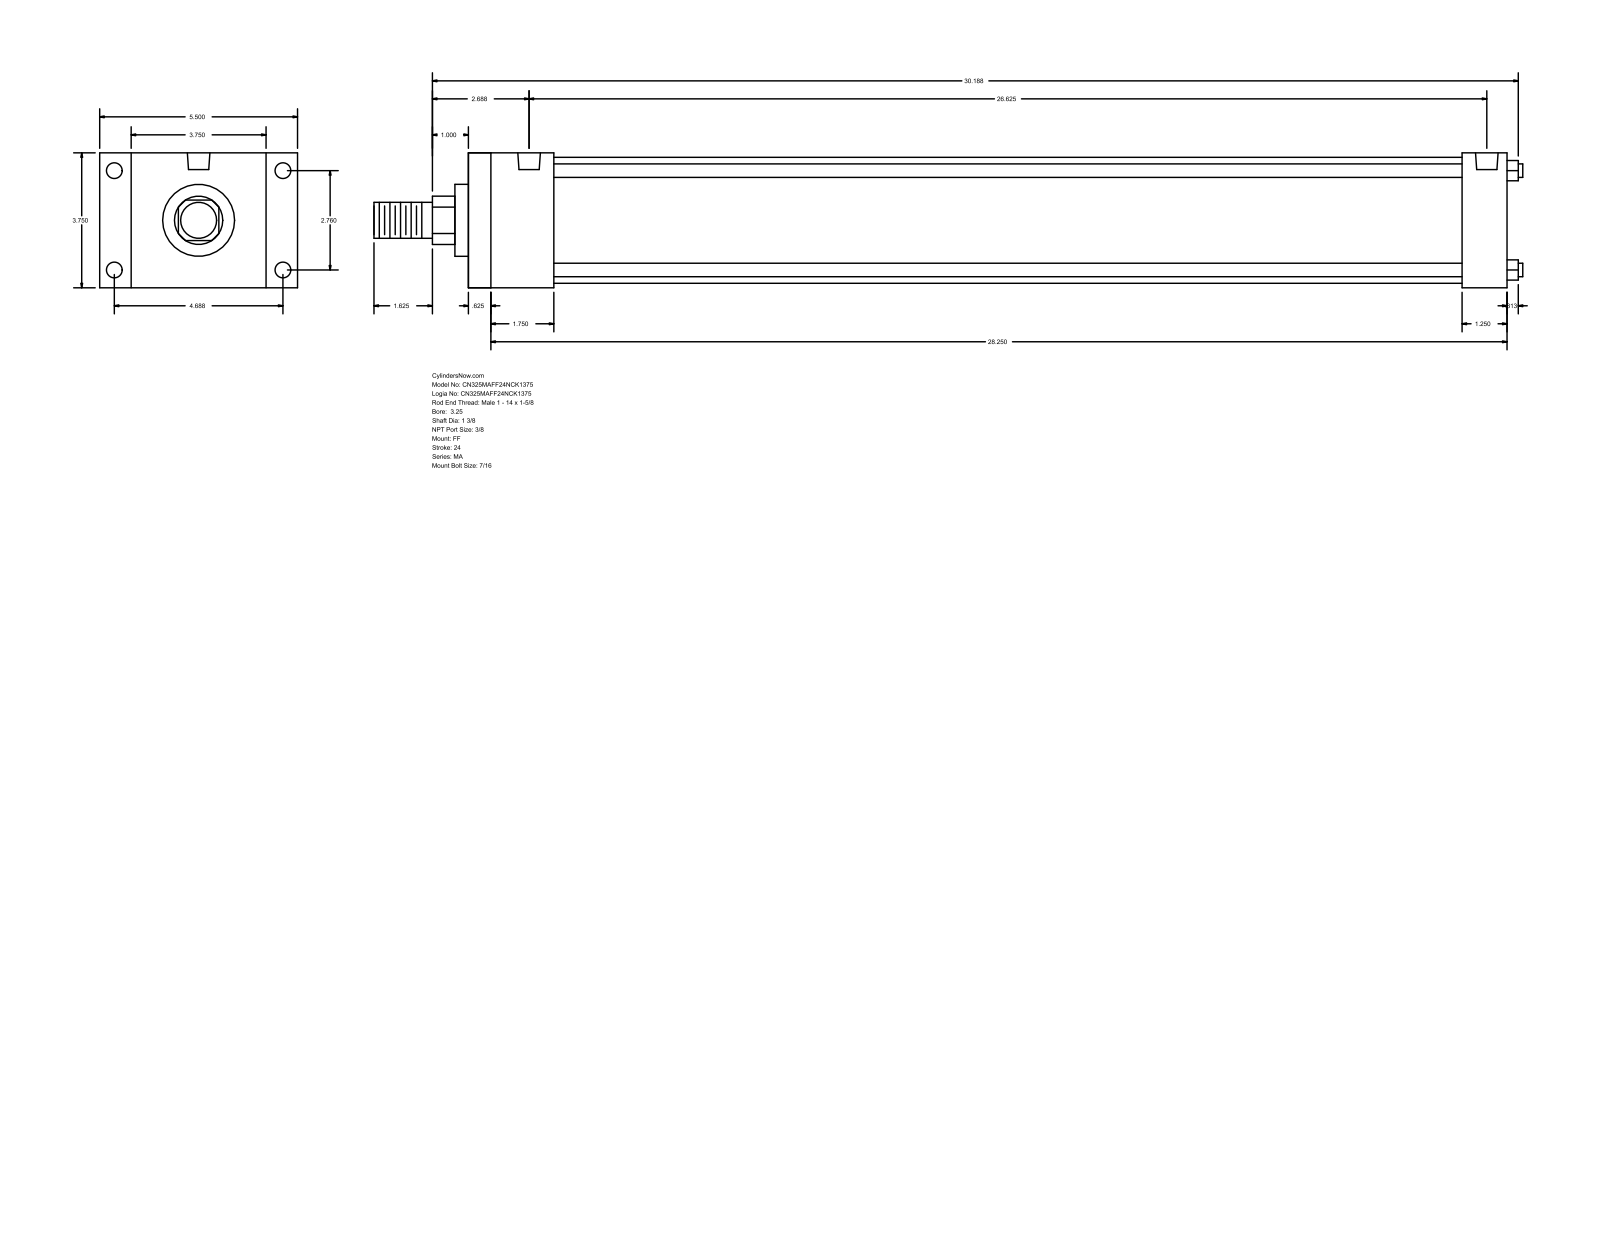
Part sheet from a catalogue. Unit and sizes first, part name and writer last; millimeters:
Units: millimetres
Overall size (bounding box): 811.21 × 139.7 × 95.25
Round holes (diameter × count): ⌀11.11 ×8, ⌀15.93 ×2
Round bosses / shafts (diameter × count): ⌀9.53 ×4, ⌀88.9 ×1, ⌀50.8 ×1, ⌀34.92 ×1, ⌀25.4 ×1
Partial cylindrical surfaces — rounded edges, fillets, slot ends (radius × count): R17.06 ×1
Main face-to-face distances: 95.24, 733.43, 15.87, 717.56, 22.23, 117.47, 60.32, 701.68, 44.45, 685.81
Hole centre spacings: 4.77, 70.1, 119.06, 138.16, 666.74, 671.51, 676.28
Bodies: 0 solids, 92 faces (64 planar, 28 cylindrical, 0 other)
Part name (STEP PRODUCT): MA_FF__0325_1.375
STEP written by: GSSL Pune (CONFIG_CONTROL_DESIGN)
